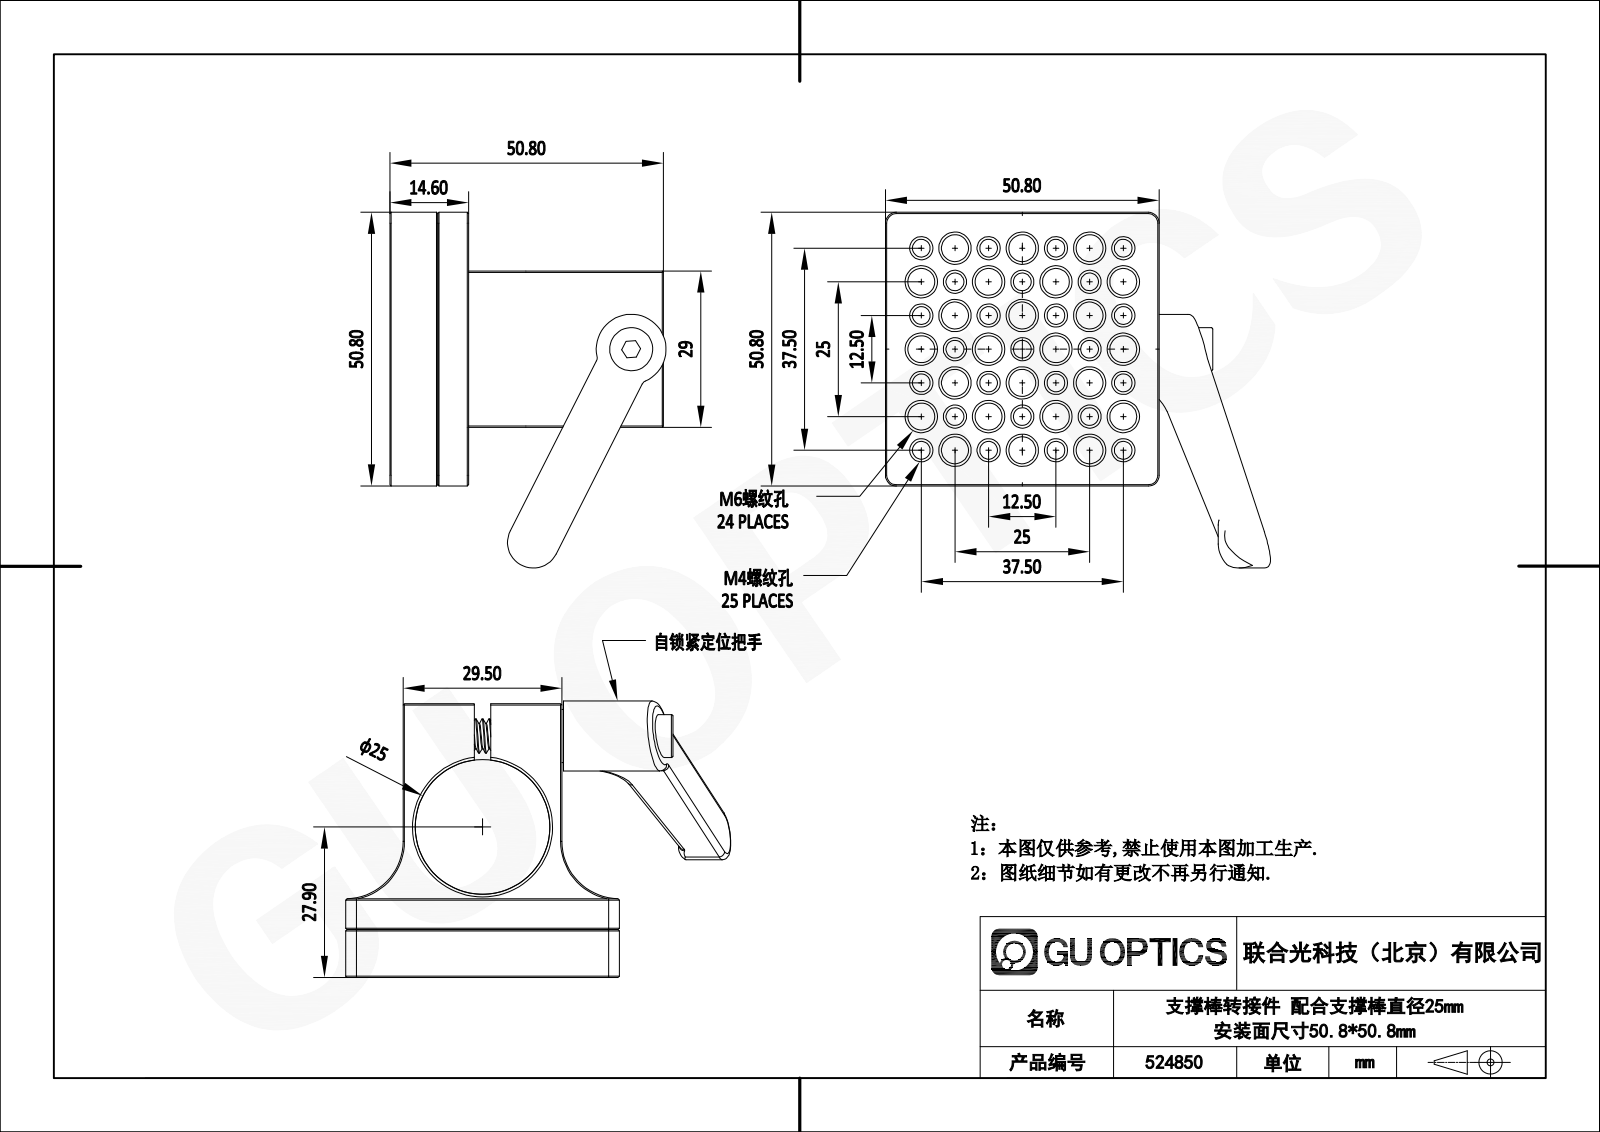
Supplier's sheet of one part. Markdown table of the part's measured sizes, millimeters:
| quantity | value |
| --- | --- |
| part name | 1.4.3.26-ZGZ-1.0-JK; 接杆安装夹块安装板，零部件，A_1.4.3.26.2，1.0英寸接杆安装夹块安装板，零部件，A; 接杆安装夹块固定座，零部件，A_1.4.3.26.1，1.0英寸接杆安装夹块固定座，零部件，A |
| STEP written by | SolidWorks 2021 (CONFIG_CONTROL_DESIGN) |
| units | millimeters |
| bodies | 8 solids, 604 faces (116 planar, 196 cylindrical, 292 other) |
| overall size | 71.48 × 66 × 51.28 |
| volume | 54 026 mm³ |
| surface area | 28 207 mm² |
| round holes (diameter × count) | 3.3 × 25, 5 × 25, 4.5 × 4, 7.8 × 4, 6.6 × 1, 10.5 × 1, 25 × 1 |
| round bosses / shafts (diameter × count) | 7.2 × 4, 4 × 4, 12.95 × 1, 9.91 × 1, 8 × 1, 6.35 × 1, 3.81 × 1 |
| partial cylindrical surfaces (radius × count) | 1.02 × 4, 2 × 4, 1.27 × 2, 10.65 × 2, 0.38 × 1, 4.76 × 1, 6.35 × 1 |
| main face-to-face distances | 8.89, 50.8, 10.65, 40.15, 10.9, 39.9, 14.61, 5.72, 50.81, 41.92 |
| hole center spacings | 13.98, 12.5, 31.25, 6.25, 22.53, 19.76, 17.68, 18.75 |
